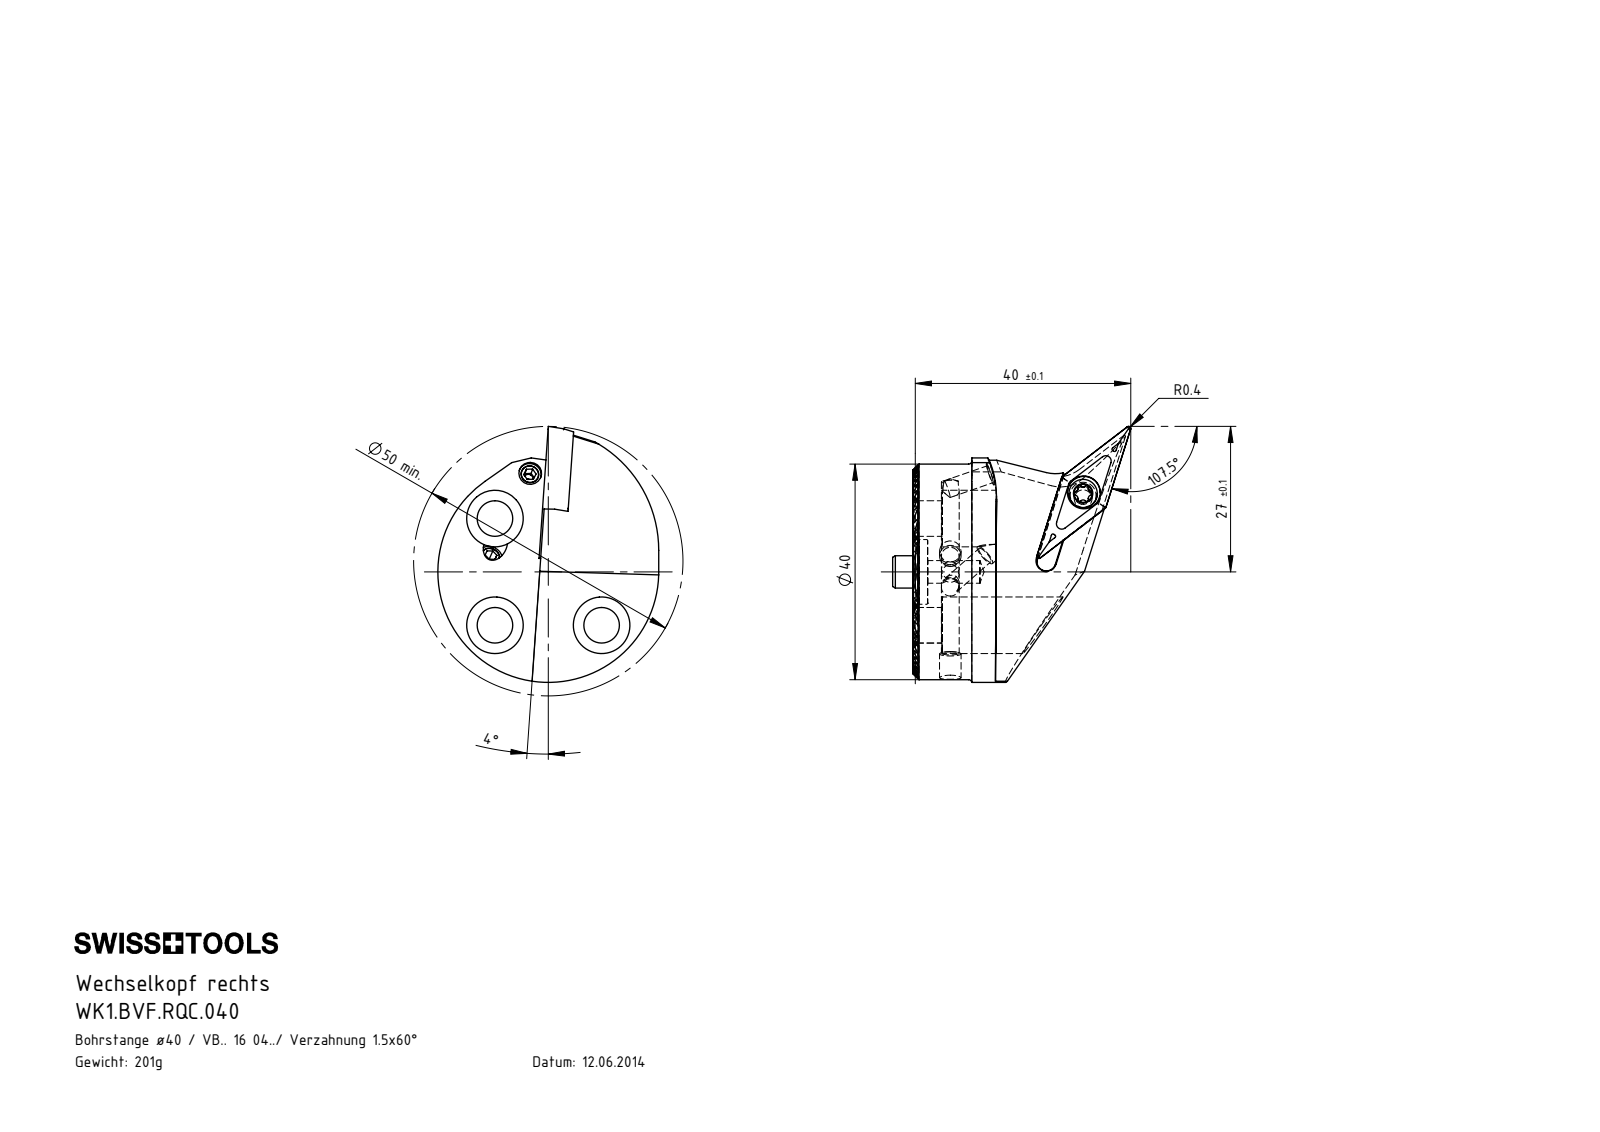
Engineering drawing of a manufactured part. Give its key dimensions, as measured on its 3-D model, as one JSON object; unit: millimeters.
{"part_name": "WCB-ER2.001.009_A; WK1-BVF.RQC.040_A_Fertigbearbeitung; VBMT160404; WKX-ER1.004.005_A_PreviewCfg (+3 more)", "step_written_by": "SolidWorks 2017 (AUTOMOTIVE_DESIGN)", "units": "millimeters", "bodies": {"solids": 10, "faces": 564, "planar": 221, "cylindrical": 198, "other": 145}, "overall_size": [47.5, 44.2, 41], "volume_mm3": 25169, "surface_area_mm2": 11024, "round_holes": [[3.3, 5], [4.2, 3], [6.6, 3], [10.5, 3], [1.7, 2], [3, 2], [4, 2], [4.4, 1], [6.1, 1], [12, 1]], "round_bosses_or_shafts": [[4, 5], [40, 1], [6, 1], [5.25, 1]], "partial_cylinders_radius": [[0.12, 26], [0.34, 6], [0.59, 6], [0.15, 2], [1.75, 1], [7, 1], [20, 1], [20.5, 1]], "face_to_face_distances": [1.3, 2.6, 3.9, 12.99, 5.2, 11.69, 9.09, 10.39, 7.79, 6.5], "hole_center_spacings": [14, 19.8, 28]}
